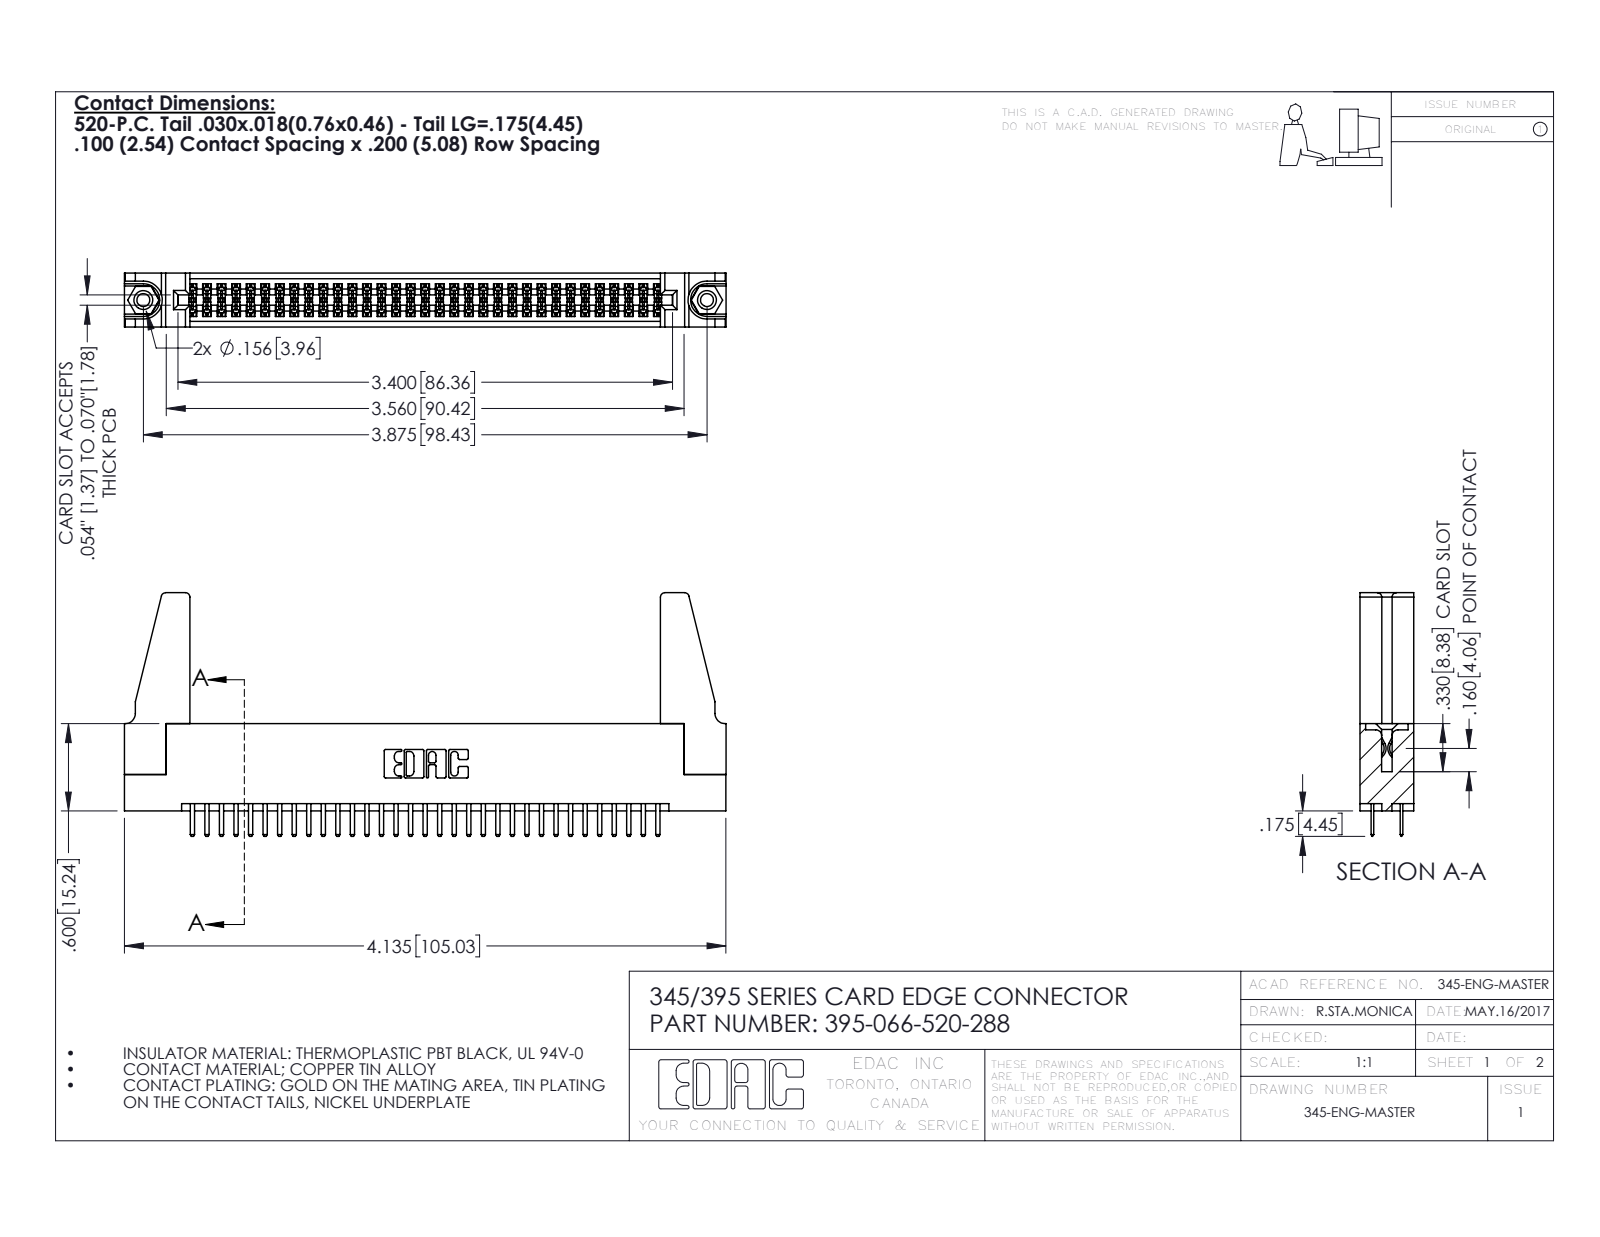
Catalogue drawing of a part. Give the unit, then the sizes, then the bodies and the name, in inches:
Units: inches
Overall size (bounding box): 4.136 × 1.675 × 0.37
Round holes (diameter × count): ⌀0.089 ×2, ⌀0.125 ×2, ⌀0.156 ×2, ⌀0.064 ×1
Round bosses / shafts (diameter × count): ⌀0.155 ×2
Partial cylindrical surfaces — rounded edges, fillets, slot ends (radius × count): R0.006 ×99, R0.01 ×70, R0.01 ×22, R0.03 ×8, R0.007 ×6, R0.031 ×6, R0.026 ×3, R0.014 ×2
Main face-to-face distances: 0.072, 0.298, 0.37, 0.2, 0.098, 0.272, 0.025, 0.225, 0.022, 0.072
Hole centre spacings: 0.27, 3.64, 3.875
Volume: 0.814 in³ · Surface area: 27.6 in²
Bodies: 71 solids, 3814 faces (2462 planar, 1336 cylindrical, 16 other)
Part name (STEP PRODUCT): 345-292-001_345-293-120; 345-250-001_345-250-001-102; 345-220-078_345-220-088; 395-066-520-288 (+1 more)
STEP written by: SolidWorks 2016 (CONFIG_CONTROL_DESIGN)
